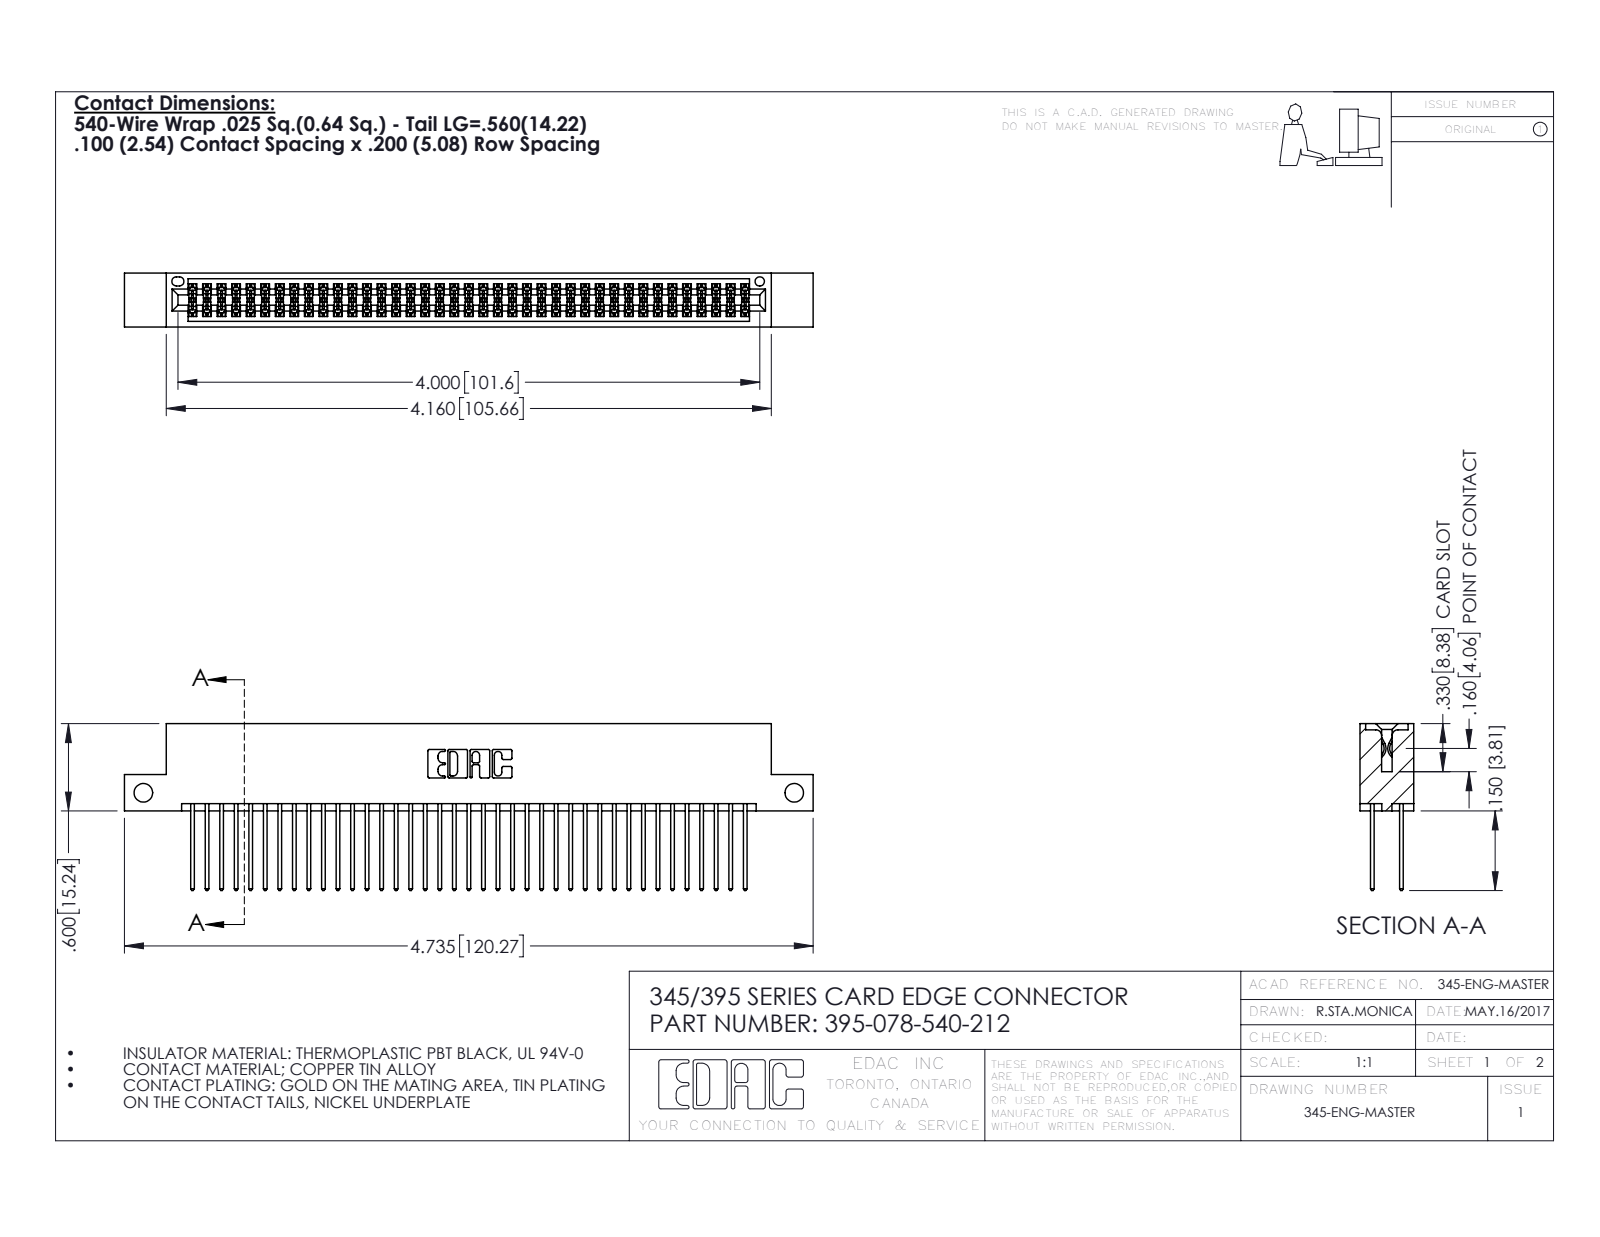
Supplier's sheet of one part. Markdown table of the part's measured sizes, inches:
| quantity | value |
| --- | --- |
| part name | 345-292-001_345-293-140; 395-078-540-212; 345 Part_Flush Mounting Lugs - Side Mount |
| STEP written by | SolidWorks 2016 (CONFIG_CONTROL_DESIGN) |
| units | inches |
| bodies | 79 solids, 4026 faces (2654 planar, 1372 cylindrical, 0 other) |
| overall size | 4.735 × 1.147 × 0.37 |
| volume | 0.724 in³ |
| surface area | 29.01 in² |
| round holes (diameter × count) | 0.128 × 2, 0.064 × 1 |
| partial cylindrical surfaces (radius × count) | 0.006 × 117, 0.01 × 78, 0.01 × 22, 0.007 × 6, 0.031 × 6, 0.026 × 3, 0.014 × 2, 0.019 × 2 |
| main face-to-face distances | 0.298, 0.072, 0.2, 0.098, 0.272, 0.025, 0.37, 0.225, 0.175, 0.149 |
| hole center spacings | 4.475 |
